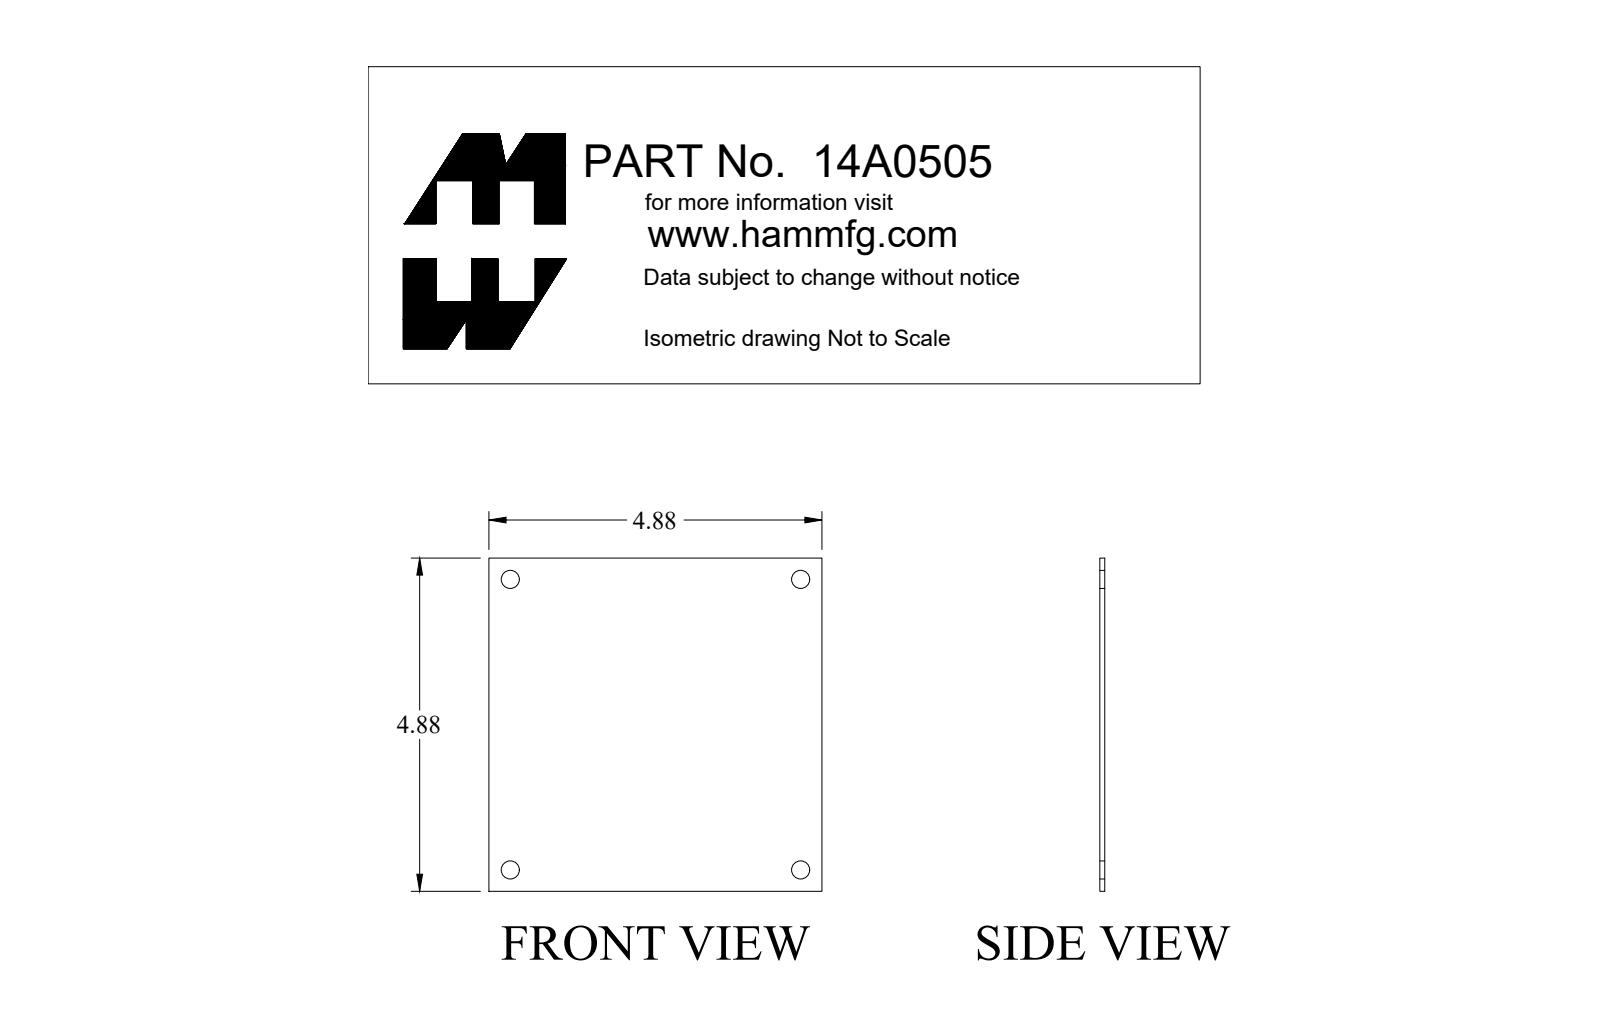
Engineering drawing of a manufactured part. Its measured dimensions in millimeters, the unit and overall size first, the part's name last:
Units: millimetres
Overall size (bounding box): 123.8 × 123.8 × 1.8
Round holes (diameter × count): ⌀6.7 ×4
Main face-to-face distances: 1.8, 123.8
Hole centre spacings: 108, 152.7
Volume: 27 780 mm³ · Surface area: 31 440 mm²
Bodies: 1 solid, 10 faces (6 planar, 4 cylindrical, 0 other)
Part name (STEP PRODUCT): 14A0505
STEP written by: SolidWorks 2018 (AUTOMOTIVE_DESIGN)
